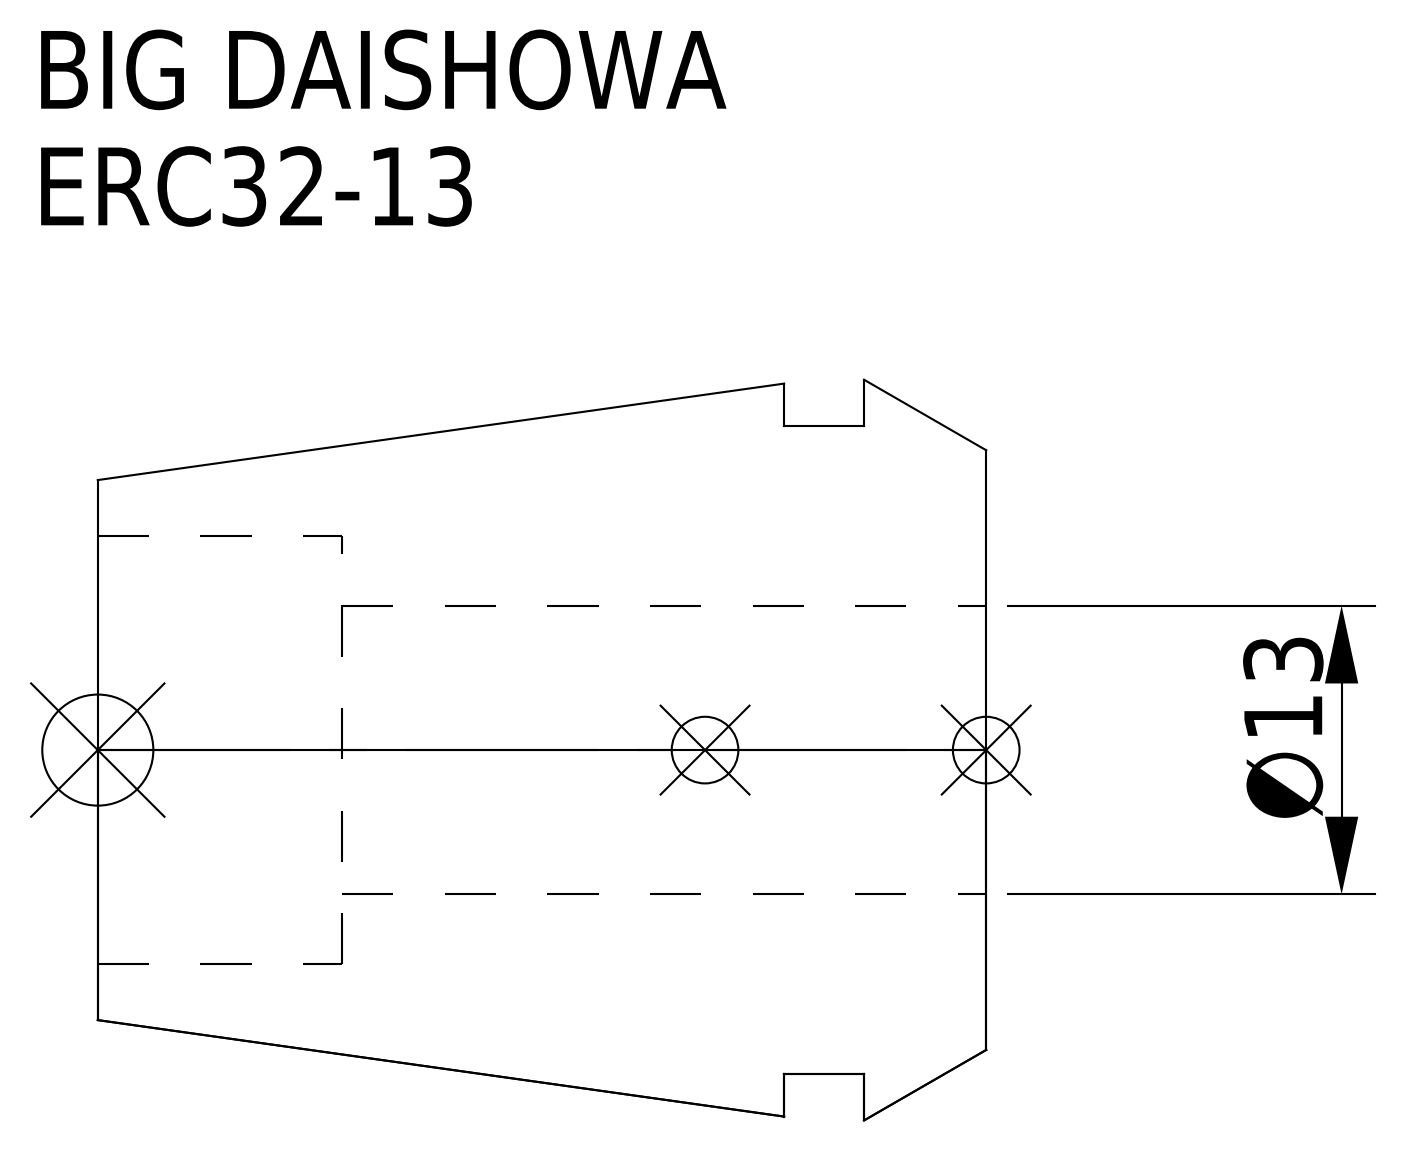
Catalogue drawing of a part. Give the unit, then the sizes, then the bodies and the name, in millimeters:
Units: millimetres
Overall size (bounding box): 40 × 33.35 × 33.35
Round holes (diameter × count): ⌀13 ×1, ⌀19.3 ×1
Round bosses / shafts (diameter × count): ⌀29.2 ×1
Main face-to-face distances: 5.5, 9.1, 3.6, 40, 34.5, 30.9, 29, 23.5, 19.9, 11
Volume: 19 375 mm³ · Surface area: 6 754 mm²
Bodies: 1 solid, 15 faces (5 planar, 6 cylindrical, 4 other)
Part name (STEP PRODUCT): ERC32-13
STEP written by: CREO PARAMETRIC BY PTC INC, 2016380 (AUTOMOTIVE_DESIGN)
